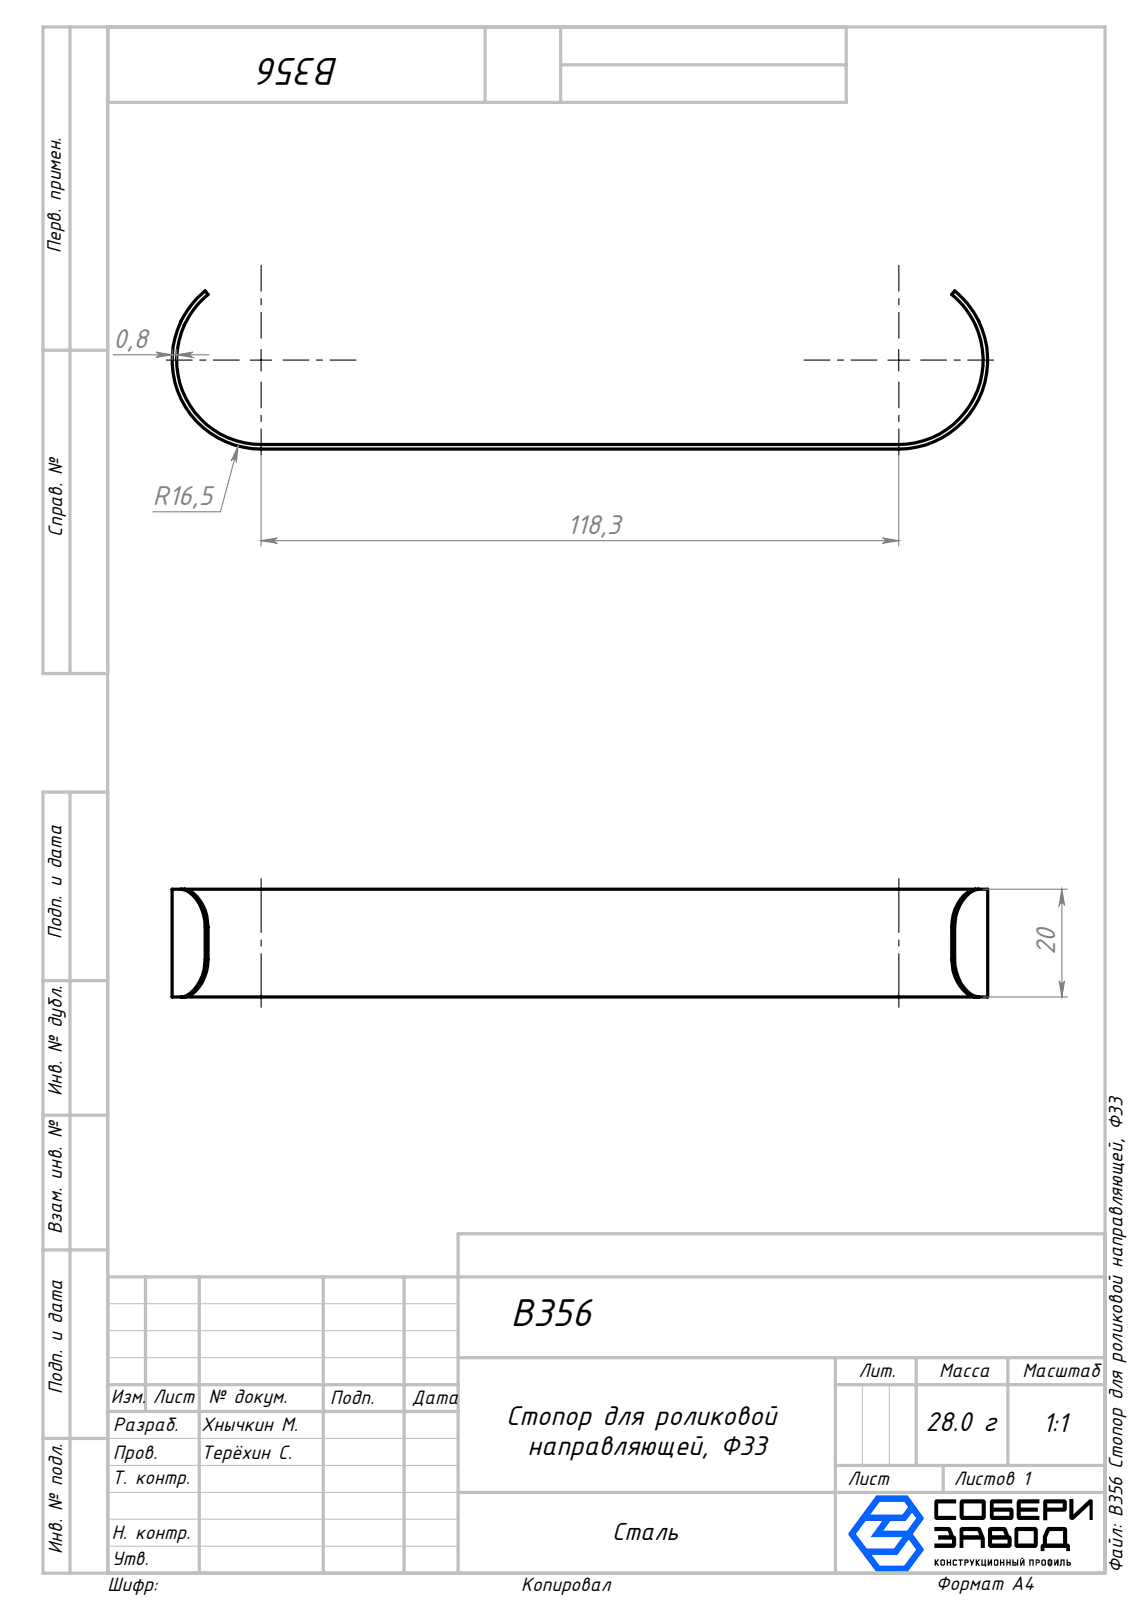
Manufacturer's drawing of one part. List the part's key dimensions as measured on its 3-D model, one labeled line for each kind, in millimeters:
Part name (STEP PRODUCT): B356 Стопор для роликовой направляющей, Ф33
STEP written by: SolidWorks 2025 (AUTOMOTIVE_DESIGN)
Units: millimetres
Bodies: 1 solid, 16 faces (6 planar, 10 cylindrical, 0 other)
Overall size (bounding box): 151.3 × 29.34 × 20
Volume: 3 321 mm³ · Surface area: 8 173 mm²
Partial cylindrical surfaces — rounded edges, fillets, slot ends (radius × count): R7 ×4, R15.65 ×2, R16.5 ×2
Main face-to-face distances: 0.85, 20
